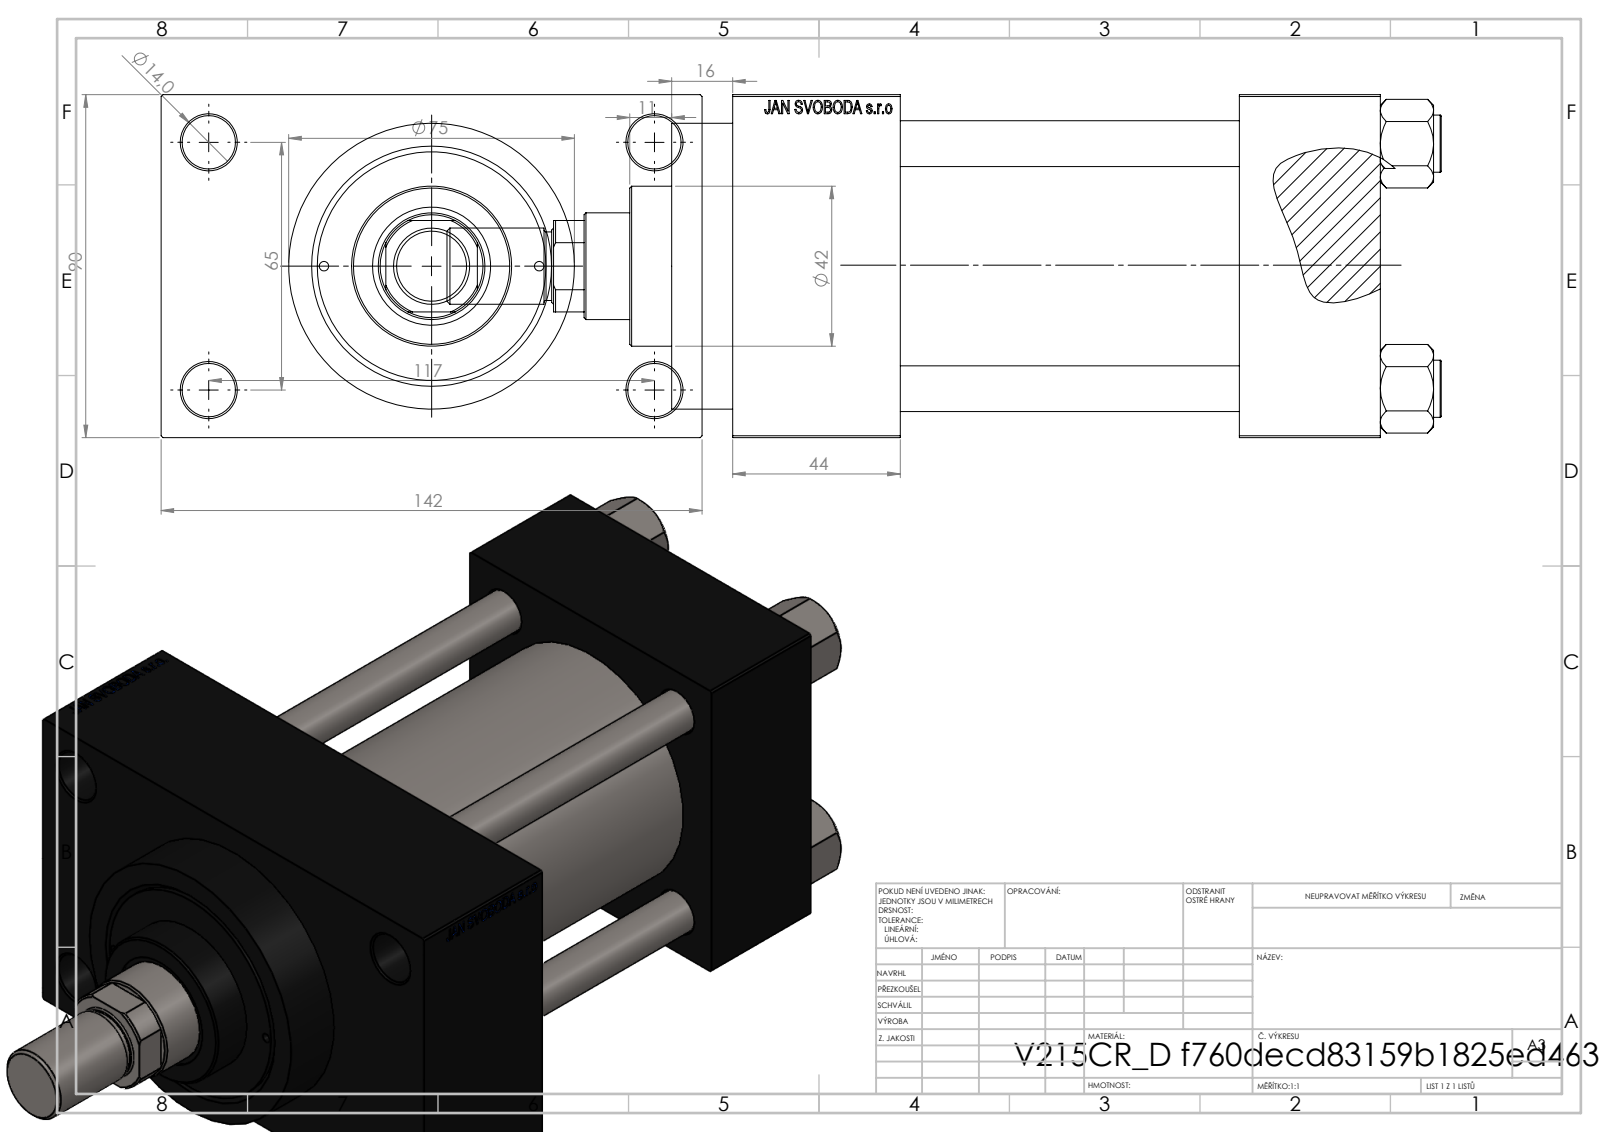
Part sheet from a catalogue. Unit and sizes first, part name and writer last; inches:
Units: inches
Overall size (bounding box): 10.276 × 5.591 × 3.543
Round holes (diameter × count): ⌀0.472 ×4, ⌀0.551 ×4, ⌀0.098 ×2, ⌀0.276 ×2, ⌀0.825 ×2, ⌀1.181 ×2, ⌀0.728 ×1, ⌀1.102 ×1, ⌀1.22 ×1, ⌀1.969 ×1, ⌀2.362 ×1, ⌀2.48 ×1
Round bosses / shafts (diameter × count): ⌀0.591 ×4, ⌀2.953 ×1, ⌀2.717 ×1, ⌀1.654 ×1, ⌀0.787 ×1, ⌀0.709 ×1
Partial cylindrical surfaces — rounded edges, fillets, slot ends (radius × count): R0.531 ×1
Main face-to-face distances: 3.543, 3.504, 1.457, 4.961, 5.236, 6.693, 1.732, 1.024, 4.567, 5.591
Hole centre spacings: 1.037, 1.275, 1.748, 1.79, 2.531, 2.635, 2.694, 2.748
Volume: 70.48 in³ · Surface area: 344.5 in²
Bodies: 12 solids, 1125 faces (503 planar, 96 cylindrical, 526 other)
Part name (STEP PRODUCT): V215CR_VCP_D; V215_VC_A; ROD_END_AH; V215CR_D_Body (+2 more)
STEP written by: SolidWorks 2019 (CONFIG_CONTROL_DESIGN)
